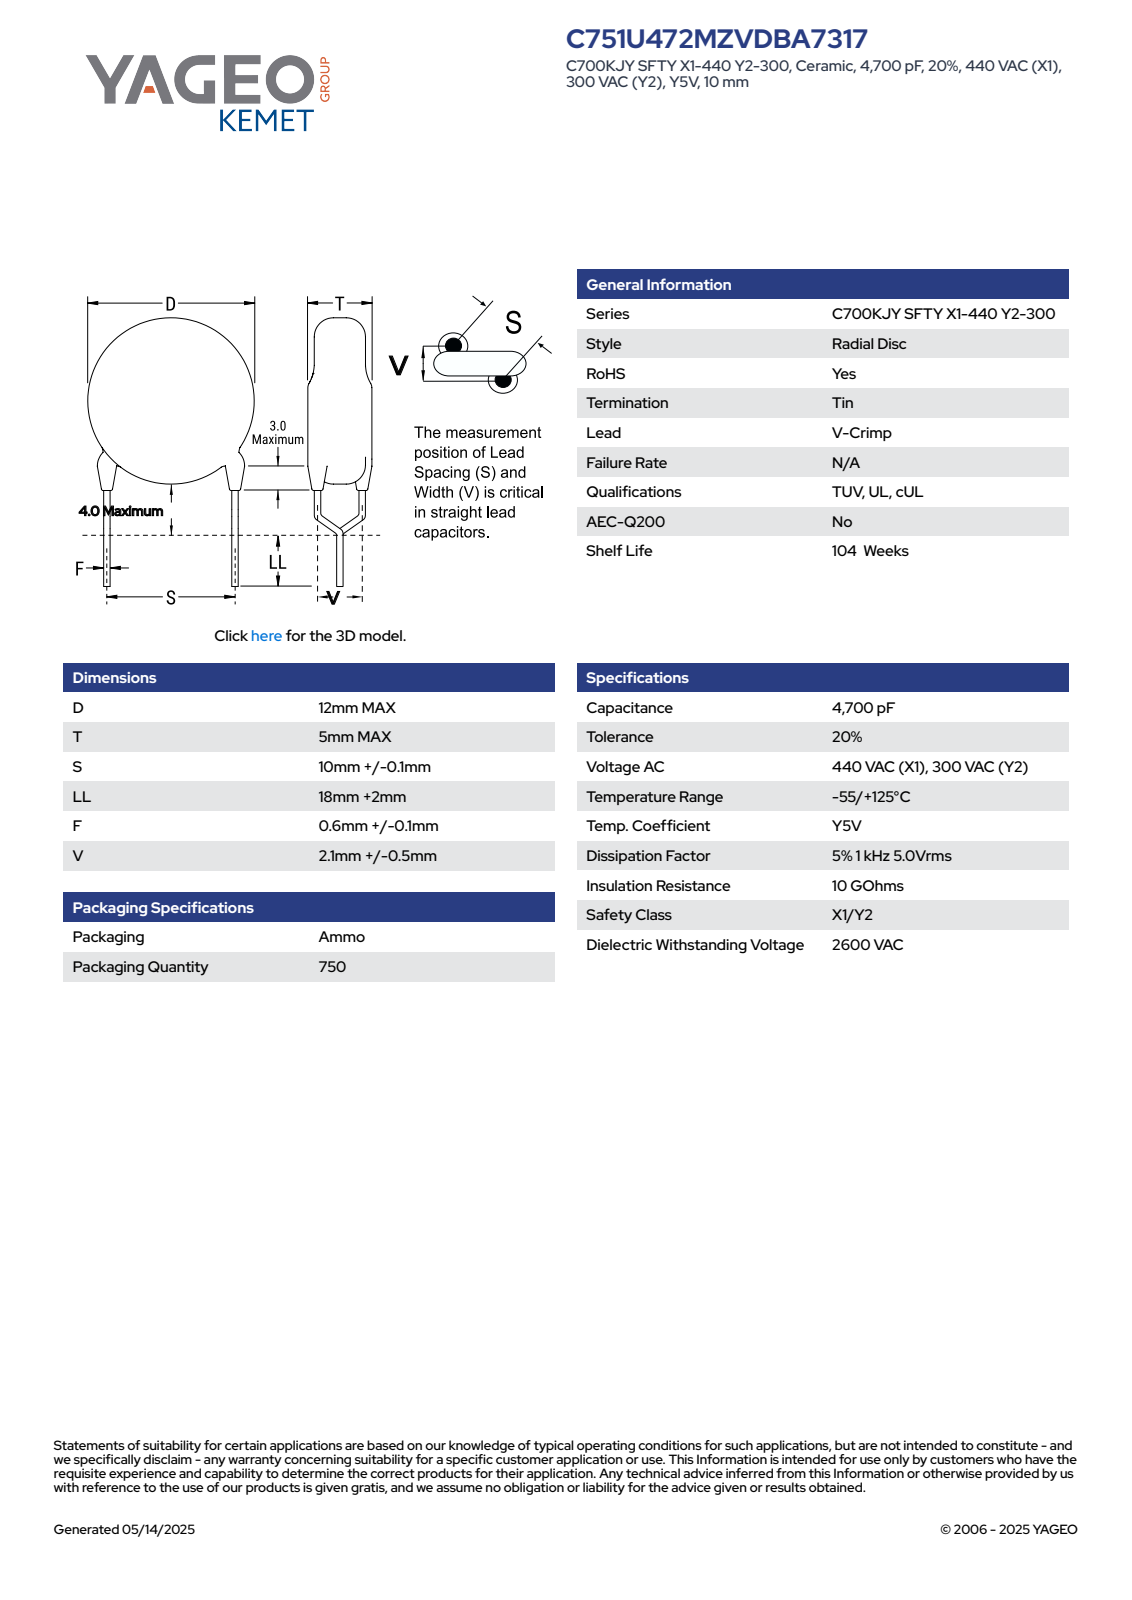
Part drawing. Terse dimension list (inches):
name: CCD_VC_12X5_D12T5S10LL18F0.7V2.1
written by: SolidWorks 2021 (AUTOMOTIVE_DESIGN)
unit: in
bodies: 4 solids, 88 faces (63 planar, 21 cylindrical, 4 other)
size: 1.181 × 0.479 × 0.197
volume: 0.035 in³; area: 0.781 in²
bosses: 6× ⌀0.028, 2× ⌀0.047, 1× ⌀0.472
rounds: 2× R0.024
face distances: 0.197, 0.709, 1.001, 0.293, 0.925, 0.217, 0.076, 0.021, 0.014, 0.312
